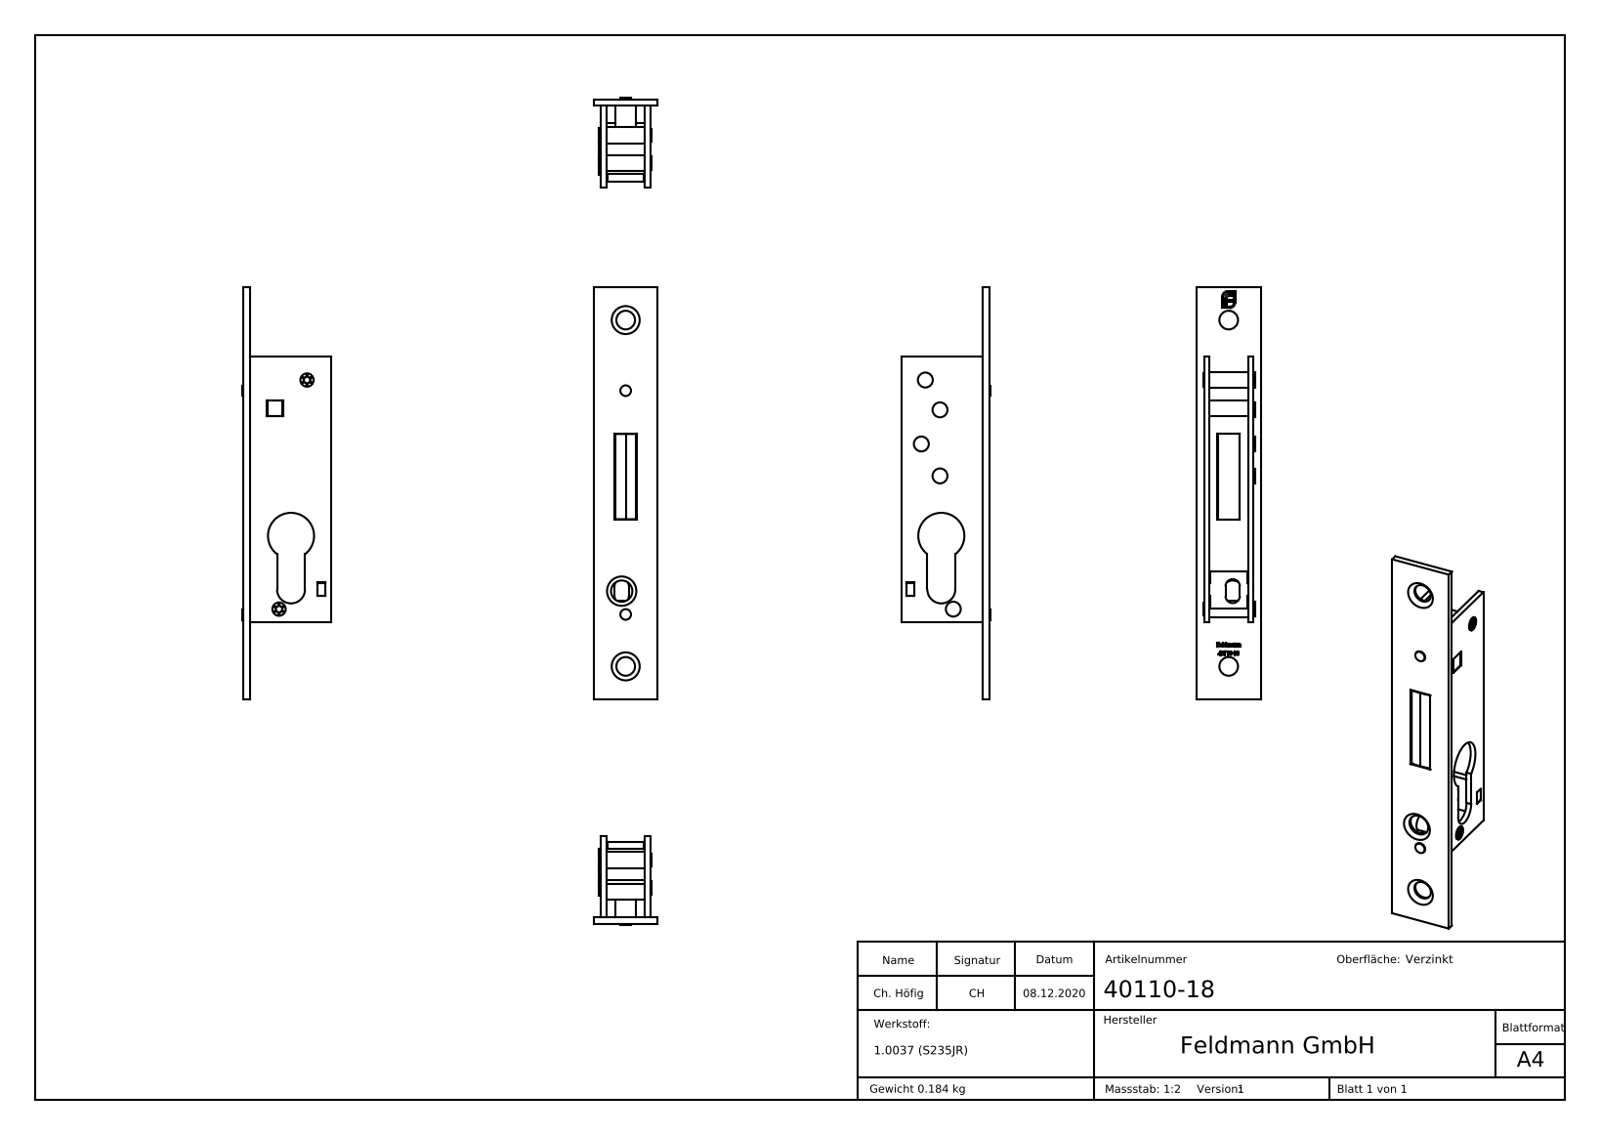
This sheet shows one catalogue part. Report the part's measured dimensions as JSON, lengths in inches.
{"part_name": "40110-18", "step_written_by": "SolidWorks 2018 (CONFIG_CONTROL_DESIGN)", "units": "inches", "bodies": {"solids": 3, "faces": 413, "planar": 231, "cylindrical": 71, "other": 111}, "overall_size": [6.102, 1.315, 0.945], "volume_in3": 1.442, "surface_area_in2": 34.05, "round_holes": [[0.276, 2], [0.315, 1]], "round_bosses_or_shafts": [[0.22, 5], [0.236, 2], [0.197, 2], [0.157, 2]], "partial_cylinders_radius": [[0.006, 12], [0.02, 12], [0.106, 2], [0.207, 1], [0.341, 1]], "face_to_face_distances": [0.65, 0.079, 0.098, 0.571, 0.728, 0.315, 0.63, 0.187, 0.443, 0.108], "hole_center_spacings": [1.114, 4.006, 5.118]}
